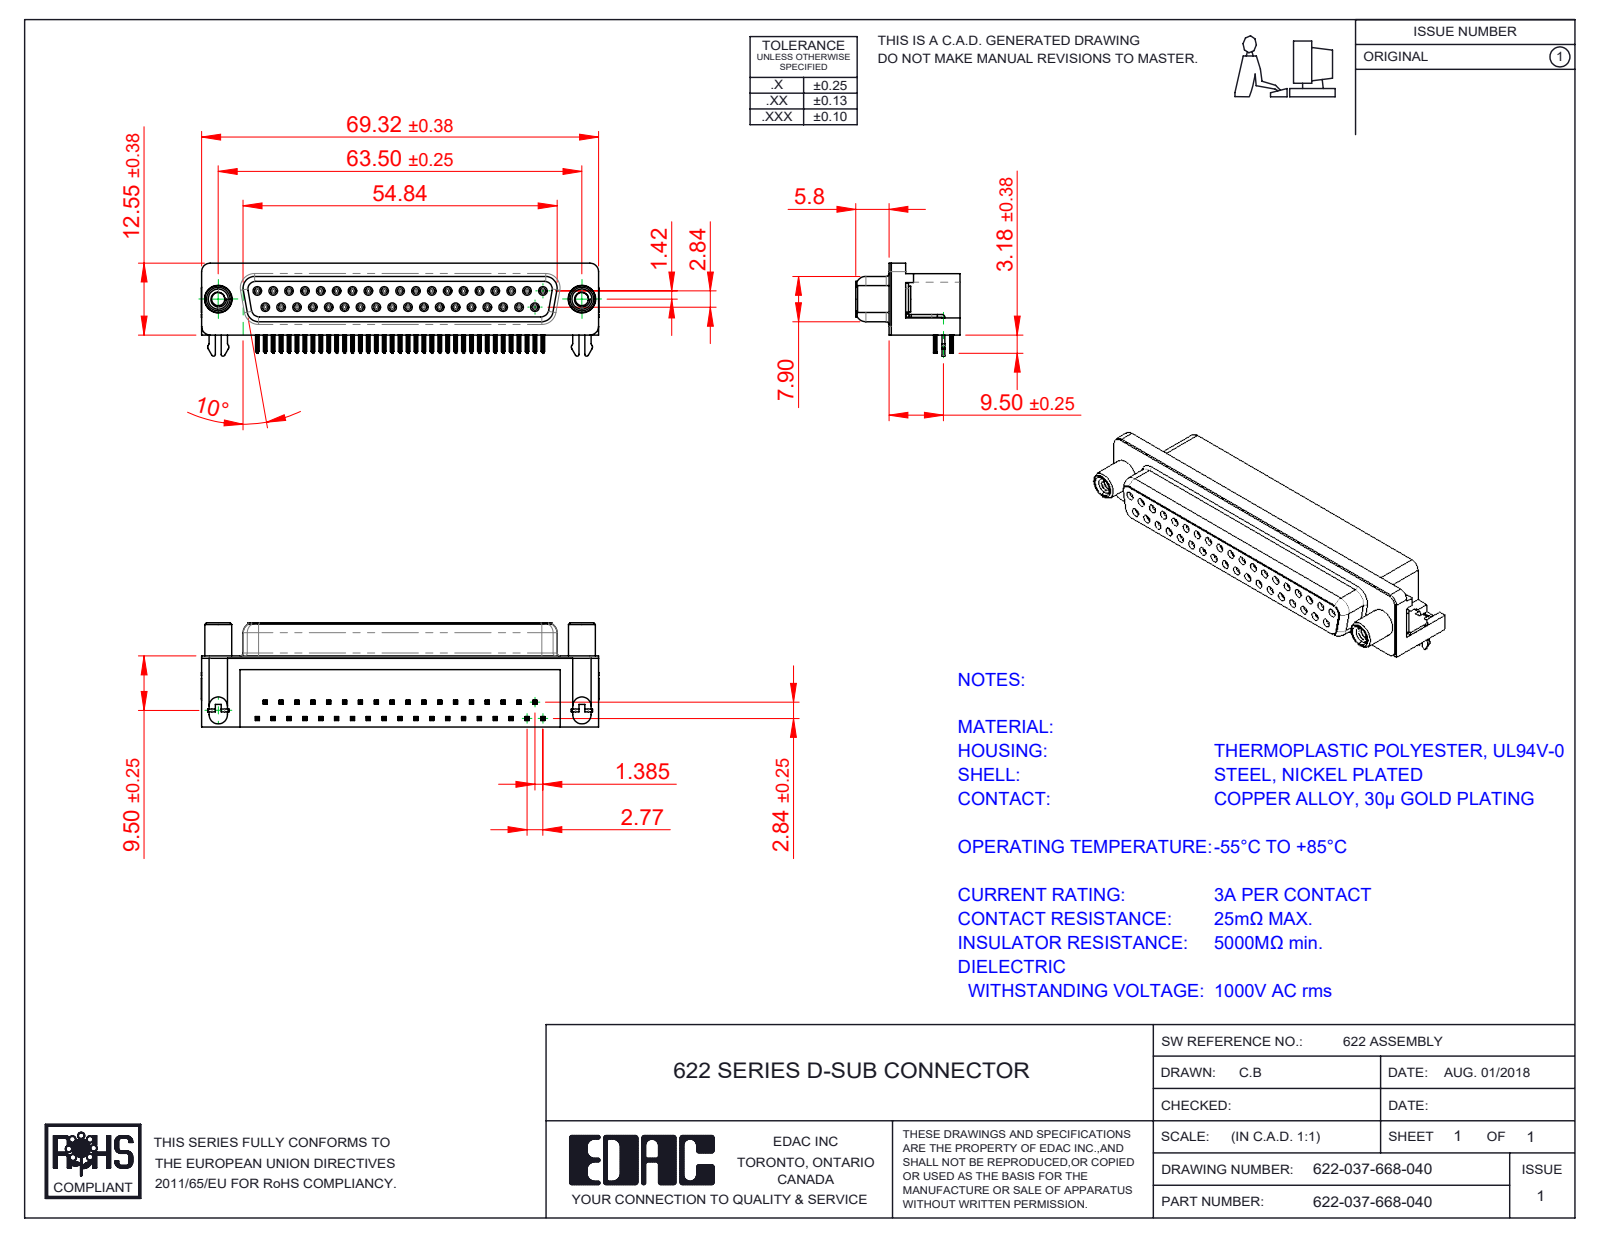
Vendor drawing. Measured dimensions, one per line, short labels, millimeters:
name: 622 Socket Bottom; 622 4 Prong Board Lock; 622 Contact Top; 622 Housing_37 Socket (+3 more)
written by: SolidWorks 2016 (CONFIG_CONTROL_DESIGN)
unit: mm
bodies: 43 solids, 5676 faces (2538 planar, 1312 cylindrical, 1826 other)
size: 69.4 × 18.2 × 16.25
volume: 10 555 mm³; area: 12 959 mm²
holes: 37× ⌀0.8, 37× ⌀0.9, 2× ⌀2, 2× ⌀2.3, 2× ⌀3.1, 2× ⌀4, 2× ⌀4.8, 2× ⌀5
bosses: 37× ⌀1.2, 2× ⌀4.9, 2× ⌀4.7, 2× ⌀4.5, 2× ⌀3.85, 2× ⌀3
rounds: 296× R0.1, 148× R0.15, 74× R0.35, 37× R0.34, 18× R0.28, 18× R1, 8× R1.35, 8× R1.6
face distances: 0.4, 12, 6.2, 10.34, 6.65, 0.85, 0.45, 2.84, 2.9, 7.05
hole spacings: 3.16, 2.77, 5.54, 8.31, 11.08, 22.16, 13.85, 19.39
